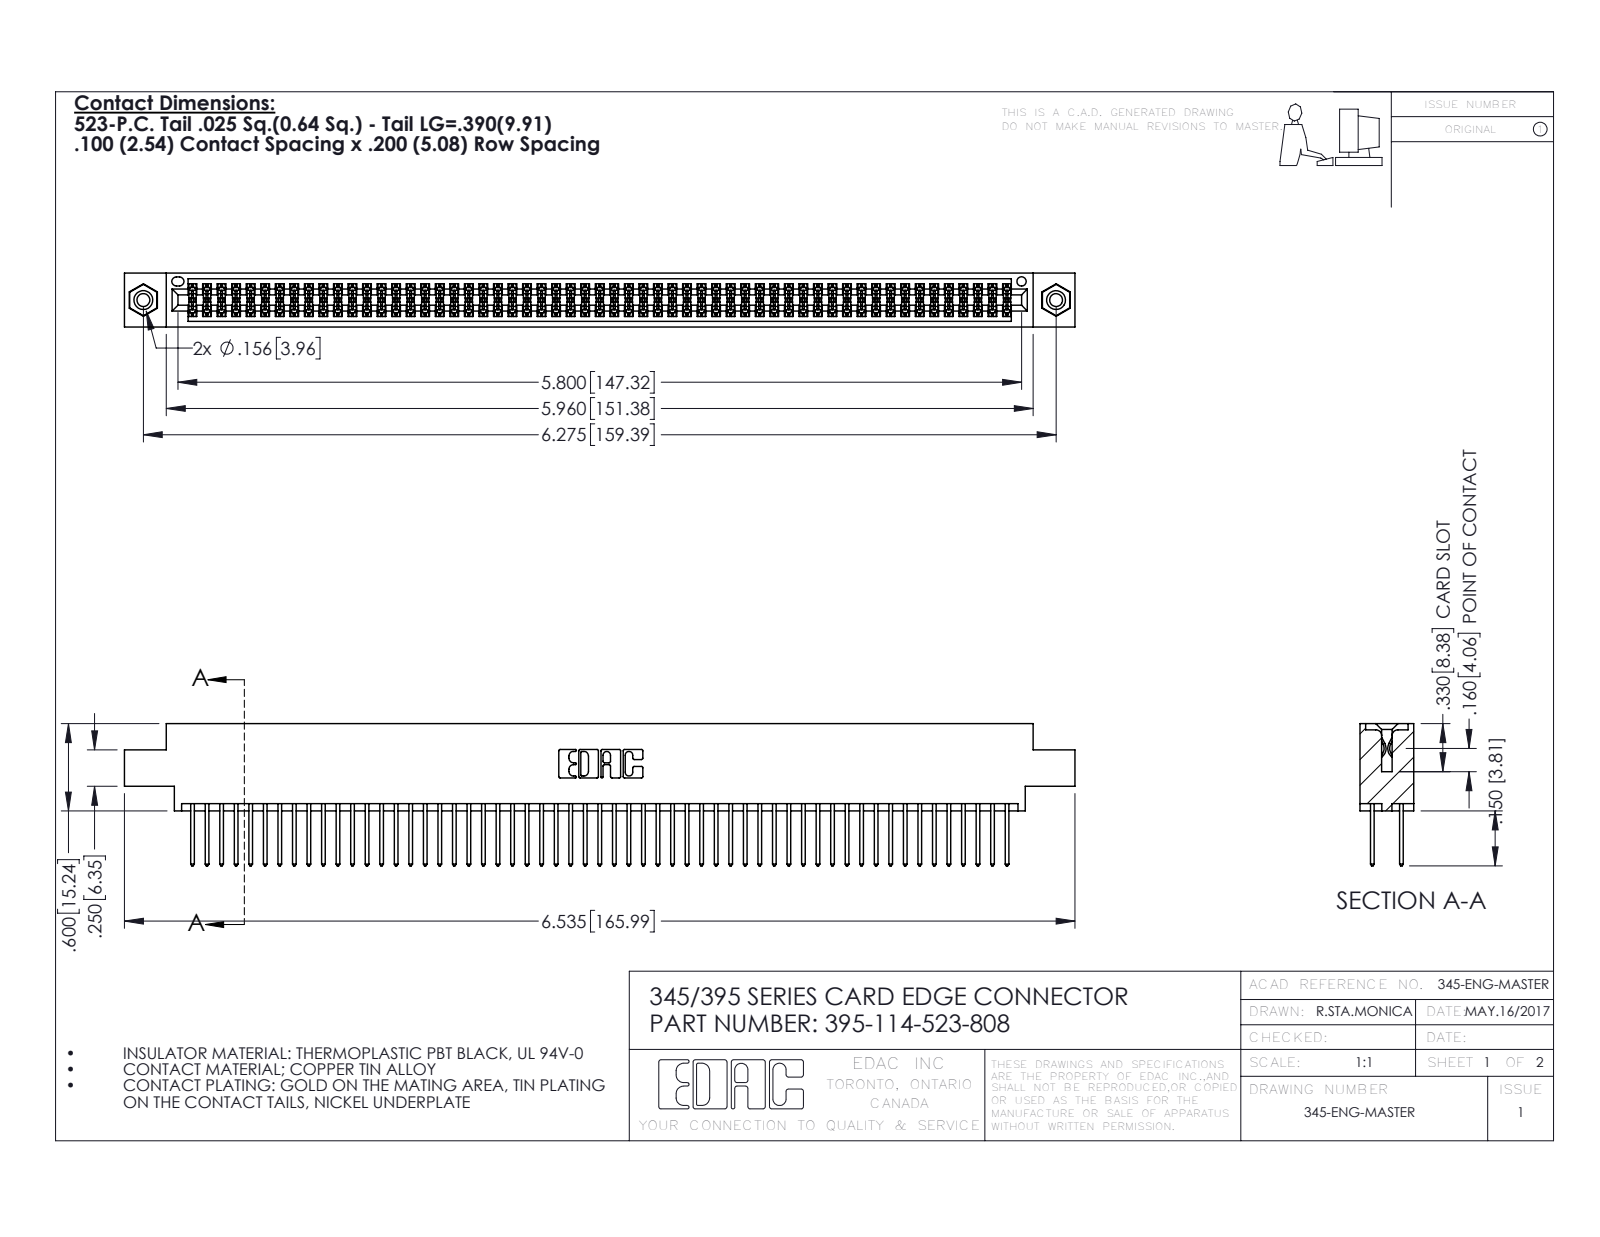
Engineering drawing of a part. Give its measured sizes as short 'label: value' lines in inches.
name: 395-114-523-808; 345 Part_0.170 Offset - 0.156 Dia-TI; 345-250-001_345-250-003-102; 345-292-001_345-293-123
written by: SolidWorks 2016 (CONFIG_CONTROL_DESIGN)
unit: in
bodies: 117 solids, 5890 faces (3878 planar, 1996 cylindrical, 16 other)
size: 6.535 × 0.977 × 0.37
volume: 0.999 in³; area: 39.84 in²
holes: 2× ⌀0.089, 2× ⌀0.125, 2× ⌀0.156, 1× ⌀0.064
bosses: 2× ⌀0.155
rounds: 171× R0.006, 114× R0.01, 22× R0.01, 6× R0.007, 6× R0.031, 3× R0.026, 2× R0.014, 2× R0.019
face distances: 0.072, 0.298, 0.2, 0.098, 0.272, 0.025, 0.37, 0.225, 0.175, 0.149
hole spacings: 0.27, 6.039, 6.275
